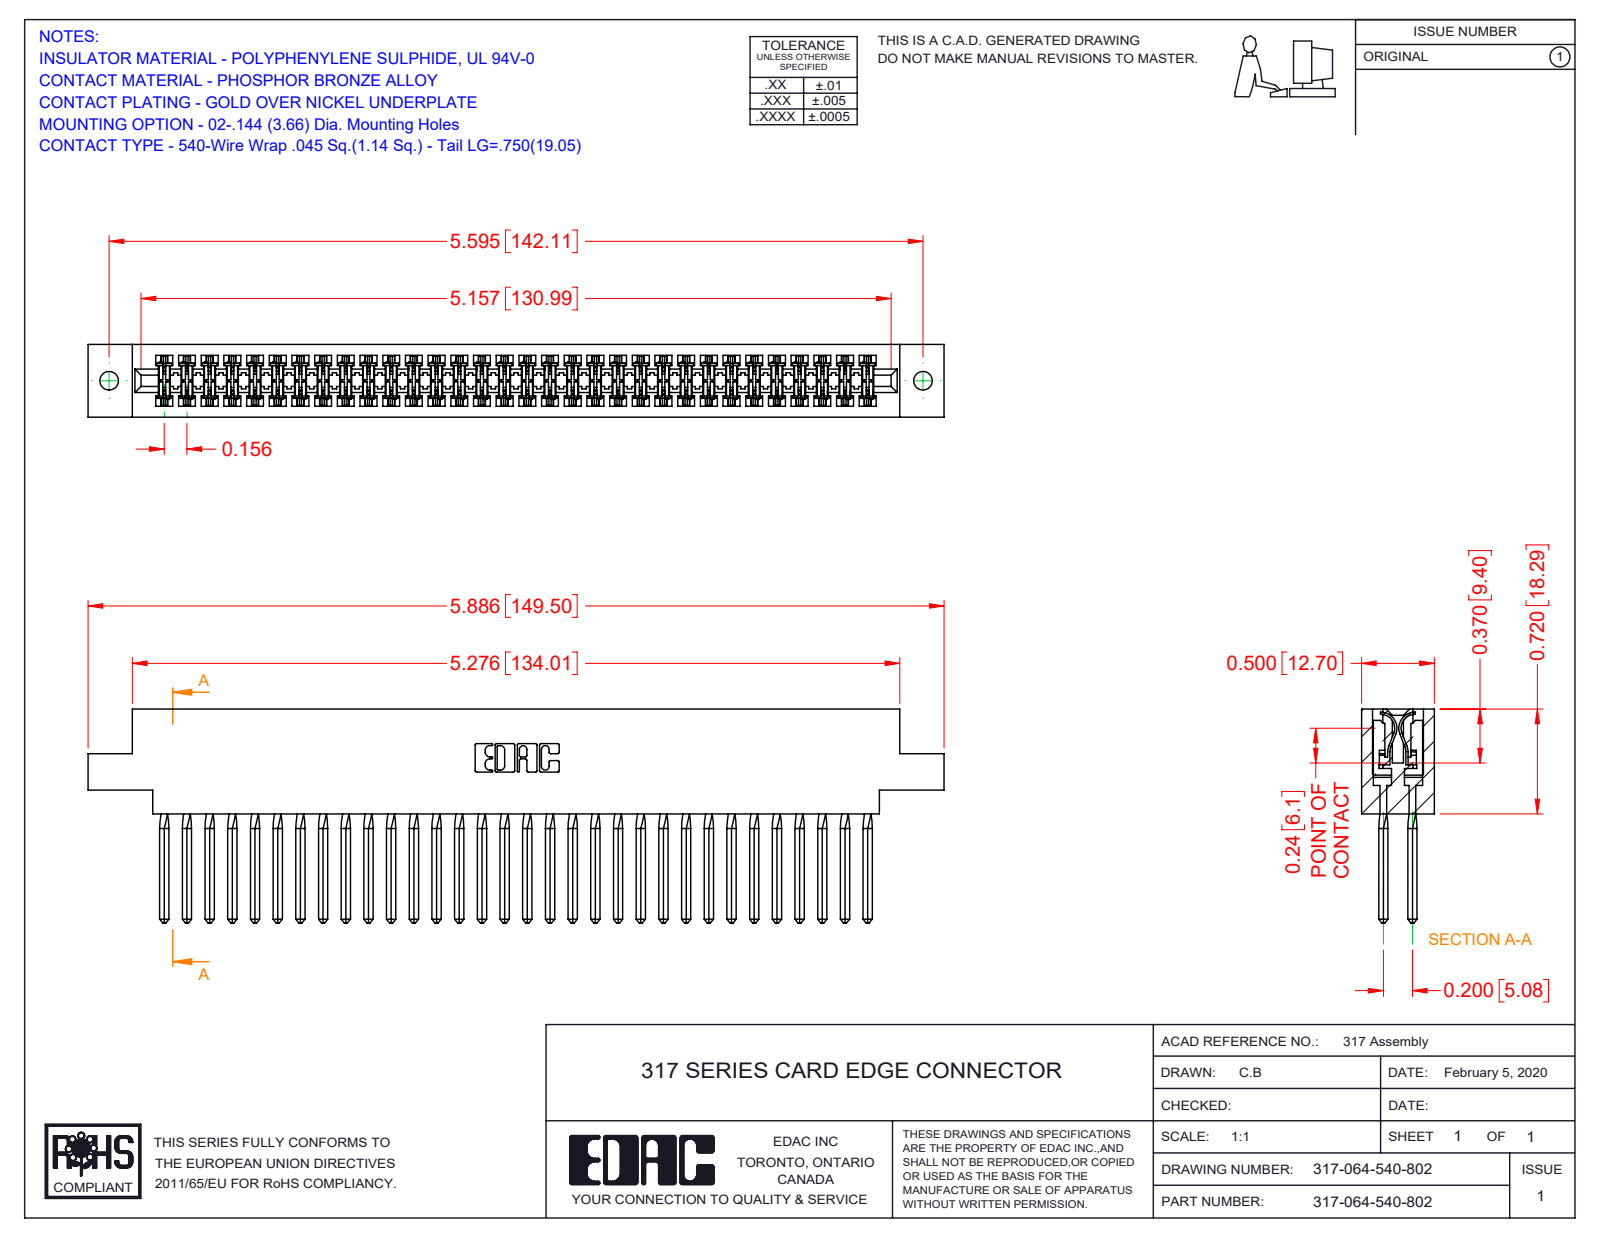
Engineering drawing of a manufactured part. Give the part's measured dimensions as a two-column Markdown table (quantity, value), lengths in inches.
| quantity | value |
| --- | --- |
| part name | 317-064-540-802; 317-290-001_540; 317 Part_.144 Dia |
| STEP written by | SolidWorks 2016 (CONFIG_CONTROL_DESIGN) |
| units | inches |
| bodies | 65 solids, 5798 faces (4730 planar, 812 cylindrical, 256 other) |
| overall size | 5.886 × 1.47 × 0.5 |
| volume | 1.508 in³ |
| surface area | 56.12 in² |
| round holes (diameter × count) | 0.128 × 2 |
| partial cylindrical surfaces (radius × count) | 0.015 × 128, 0.01 × 22, 0.007 × 6, 0.031 × 6, 0.026 × 3, 0.095 × 2, 0.1 × 2, 0.11 × 2 |
| main face-to-face distances | 0.5, 0.075, 0.425, 0.35, 0.11, 0.195, 0.094, 0.2, 0.115, 0.131 |
| hole center spacings | 5.595 |
